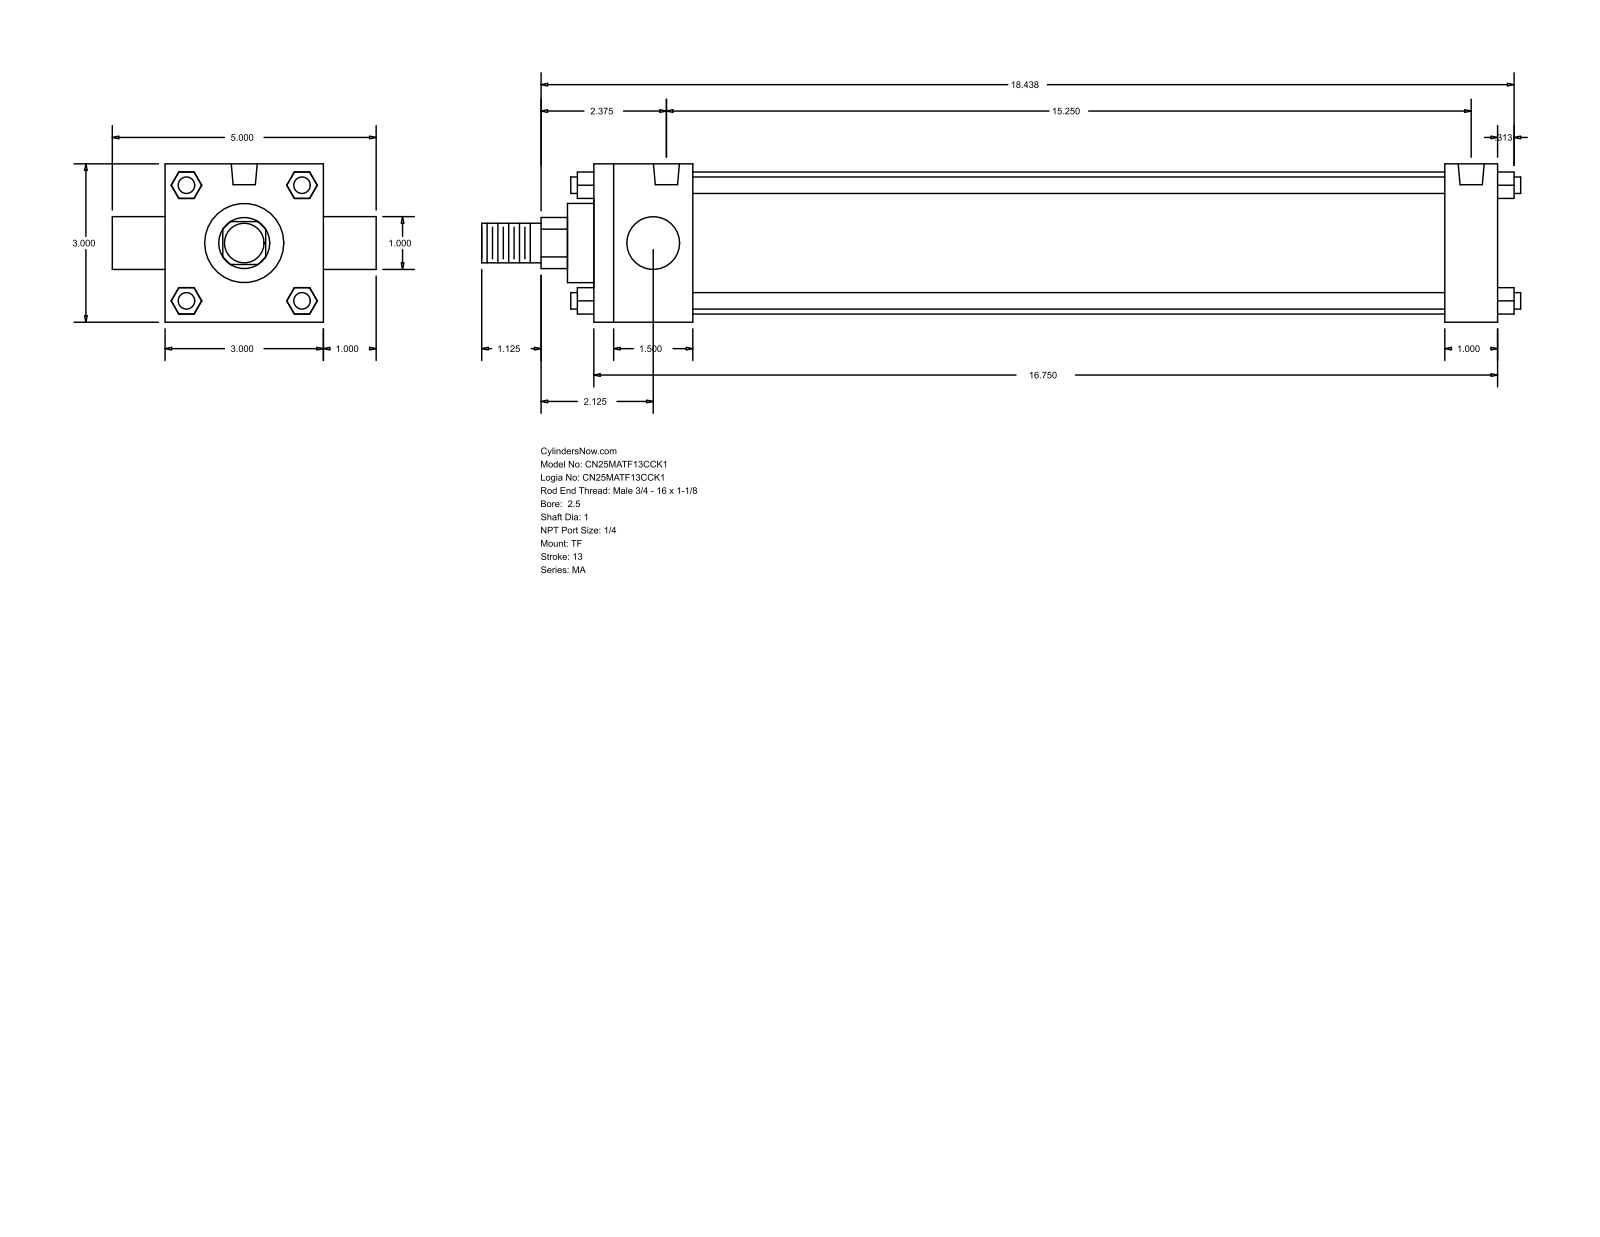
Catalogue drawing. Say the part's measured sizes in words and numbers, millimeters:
The part is named "MA_TF__0250_1". Its 3-D file was written by "GSSL Pune (CONFIG_CONTROL_DESIGN)". It is 0 solids with 120 faces: 92 planar, 28 cylindrical and 0 other. Overall it measures 500.06 by 127 by 76.2 millimeters. Round holes: 3 of diameter 7.94, 2 of diameter 12.49. Round bosses or shafts: 4 of diameter 7.94, 2 of diameter 25.4, 1 of diameter 68.33, 1 of diameter 38.1, 1 of diameter 19.05. Partial cylindrical surfaces (rounded edges, fillets, slot ends): 1 of radius 12.29. The main face-to-face distances are 76.2, 434.98, 25.4, 12.7, 47.63, 409.58, 361.95, 387.35, 101.6, 27.81. The hole center spacings are 387.35.
